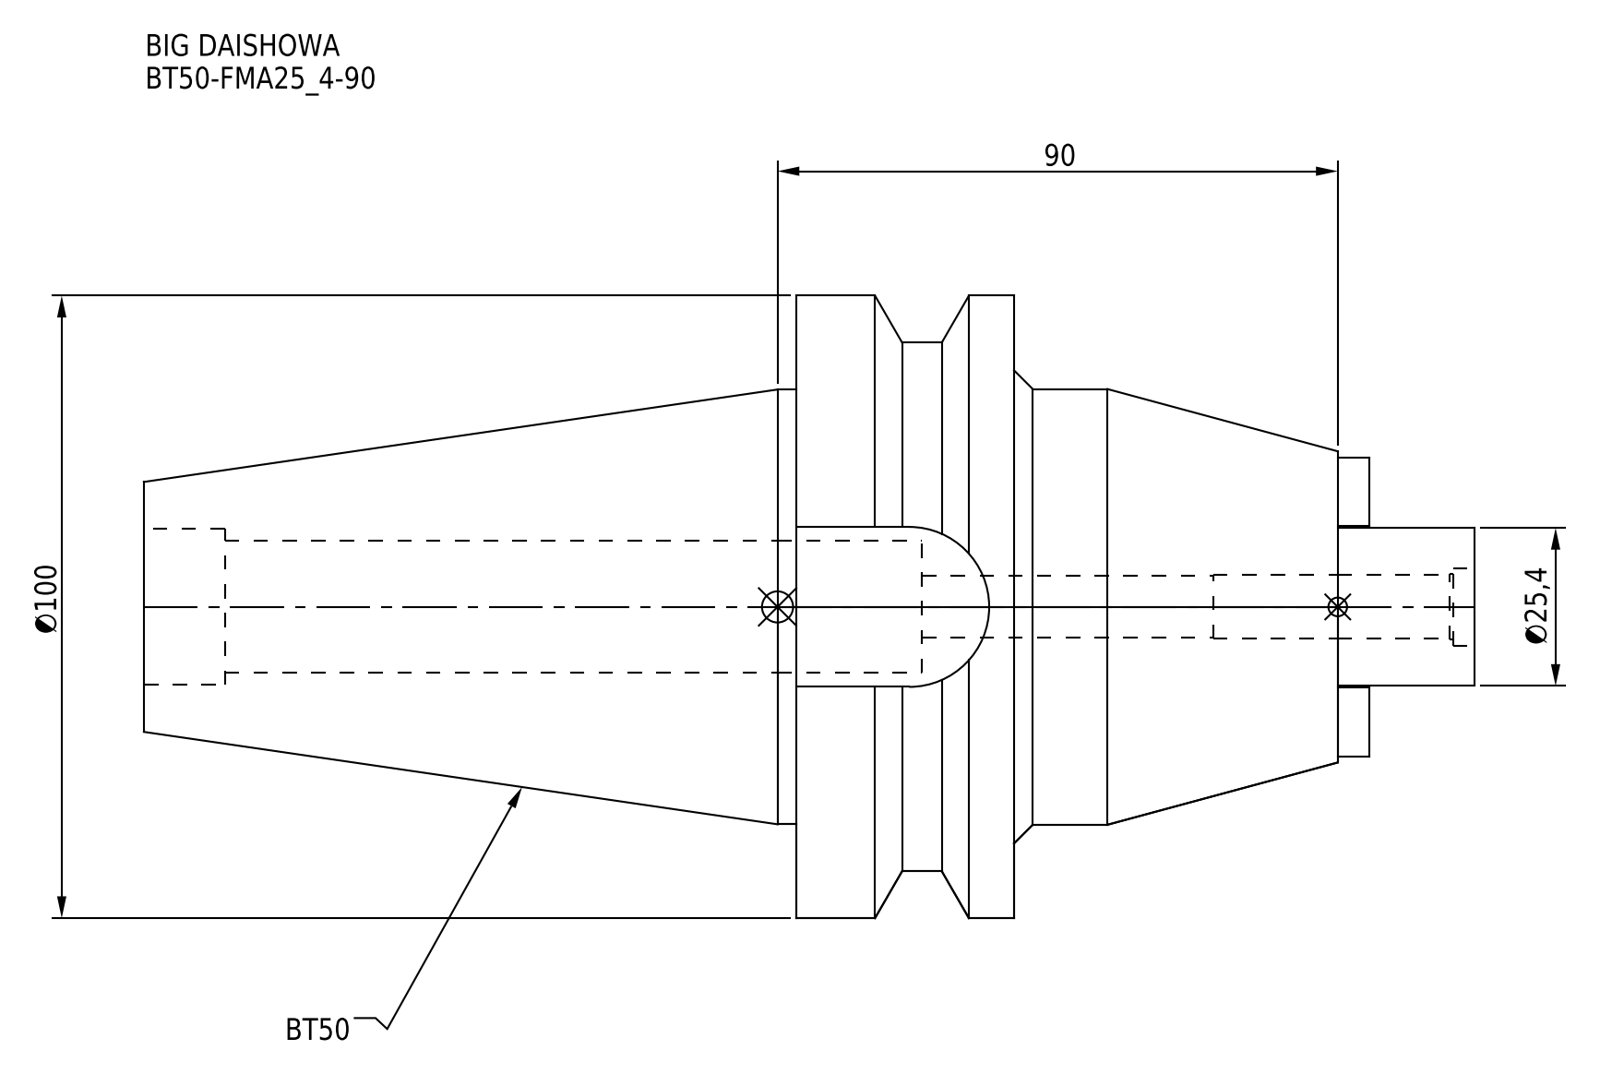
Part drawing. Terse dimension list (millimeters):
name: BT50-FMA25_4-90
written by: CREO PARAMETRIC BY PTC INC, 2016380 (AUTOMOTIVE_DESIGN)
unit: mm
bodies: 1 solid, 66 faces (26 planar, 30 cylindrical, 10 other)
size: 213.8 × 100 × 100
volume: 617 351 mm³; area: 66 736 mm²
holes: 1× ⌀10, 1× ⌀10.25, 1× ⌀10.5, 1× ⌀12.5, 1× ⌀21.2, 1× ⌀25
bosses: 1× ⌀100, 1× ⌀85, 1× ⌀70, 1× ⌀69.85, 1× ⌀25.4
rounds: 1× R12.85
face distances: 35, 52, 87, 191.8, 139.8, 104.8, 70.8, 25.7, 22, 74
